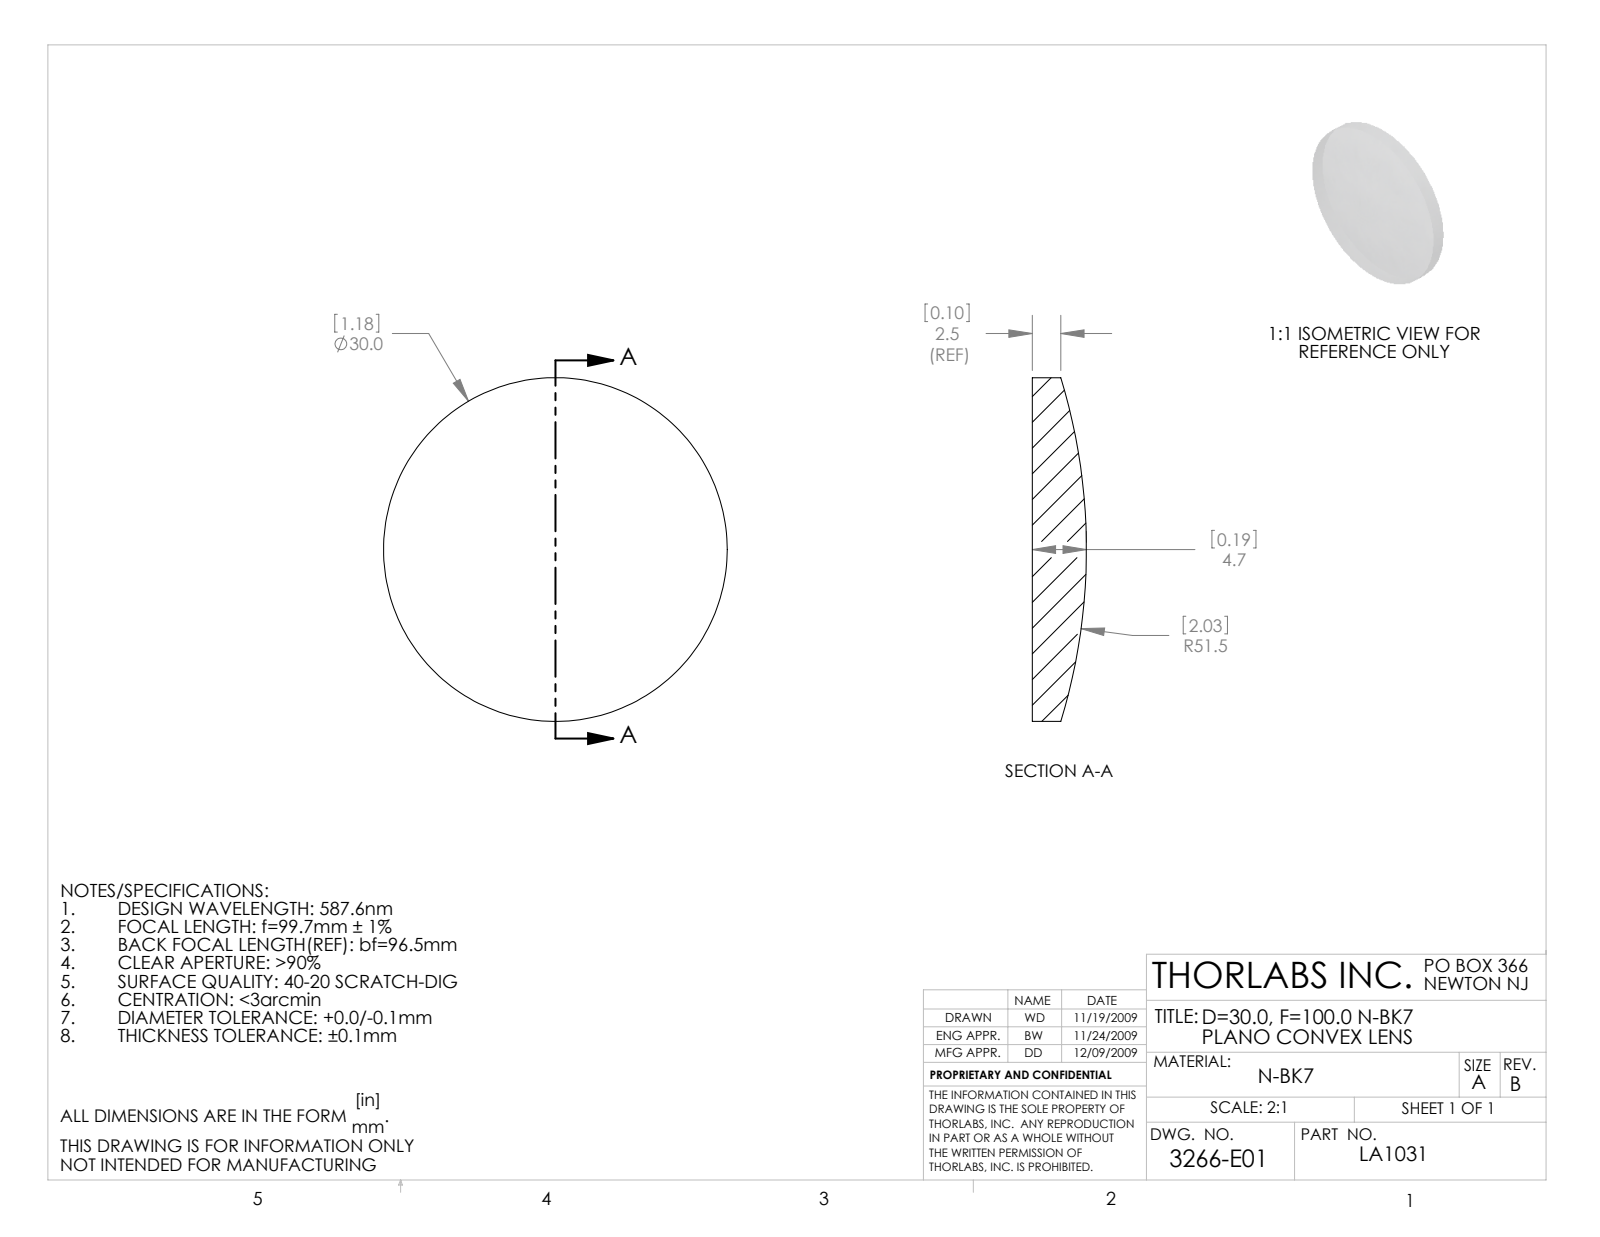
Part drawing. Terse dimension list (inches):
name: 3266-E0W
written by: SolidWorks 2009 (AUTOMOTIVE_DESIGN)
unit: in
bodies: 1 solid, 5 faces (1 planar, 2 cylindrical, 2 other)
size: 1.181 × 1.181 × 0.186
volume: 0.156 in³; area: 2.581 in²
bosses: 1× ⌀1.181
